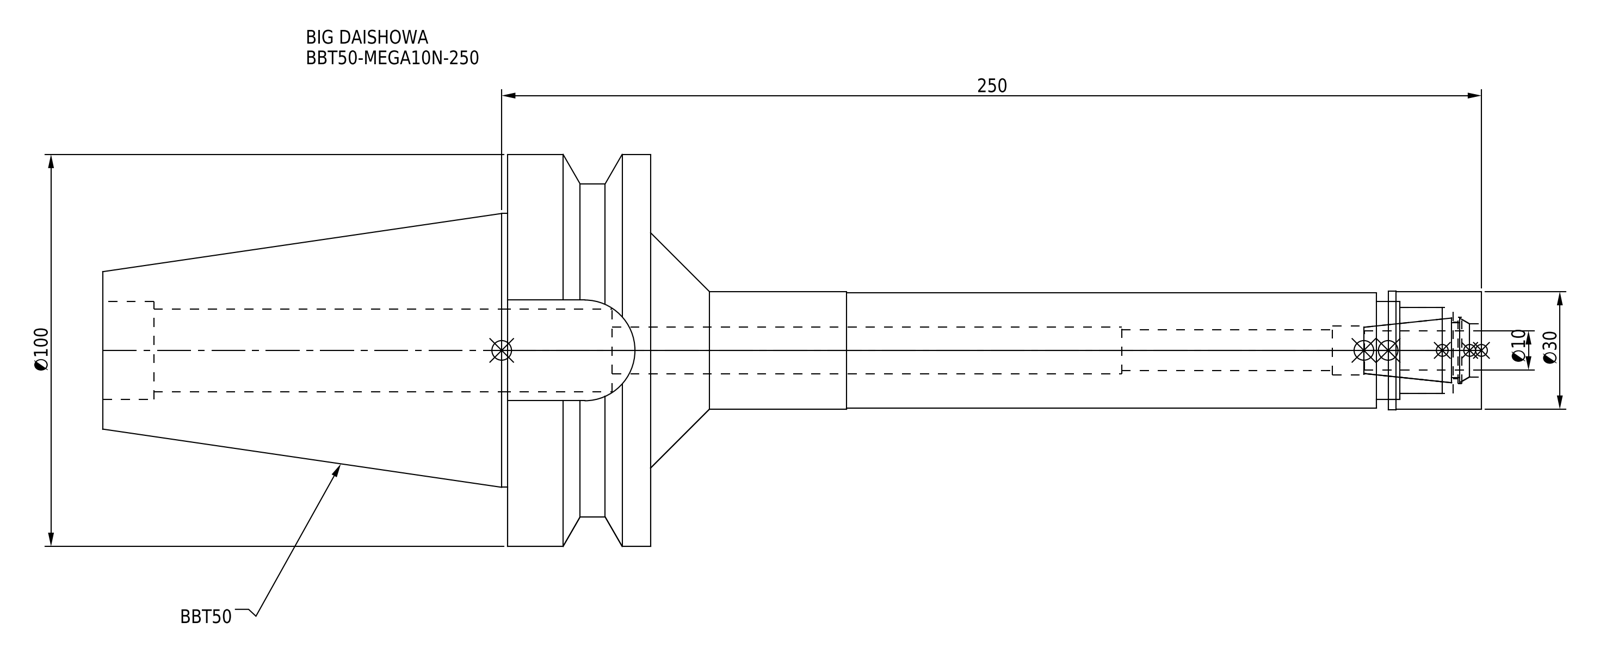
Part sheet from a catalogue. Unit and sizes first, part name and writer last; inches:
Units: inches
Overall size (bounding box): 13.85 × 3.937 × 3.937
Round holes (diameter × count): ⌀0.409 ×1, ⌀0.472 ×1, ⌀0.492 ×1, ⌀0.531 ×1, ⌀0.571 ×1, ⌀0.669 ×1, ⌀0.835 ×1, ⌀0.866 ×1, ⌀0.984 ×1
Round bosses / shafts (diameter × count): ⌀3.937 ×1, ⌀3.346 ×1, ⌀2.75 ×1, ⌀1.193 ×1, ⌀1.181 ×1, ⌀1.161 ×1
Partial cylindrical surfaces — rounded edges, fillets, slot ends (radius × count): R0.506 ×1
Main face-to-face distances: 1.437, 5.504, 4.067, 2.787, 8.346, 9.783, 13.85, 1.012, 5.118, 8.732
Volume: 35.76 in³ · Surface area: 131.3 in²
Bodies: 2 solids, 82 faces (24 planar, 44 cylindrical, 14 other)
Part name (STEP PRODUCT): BBT50-MEGA10N-250-100-FreeParts; BBT50-MEGA10N-250; DXF_TEMP_ASSY_ASM_4_ASM.stp; BBT50-MEGA10N-250-100.stp (+3 more)
STEP written by: SolidWorks 2019 (CONFIG_CONTROL_DESIGN)
